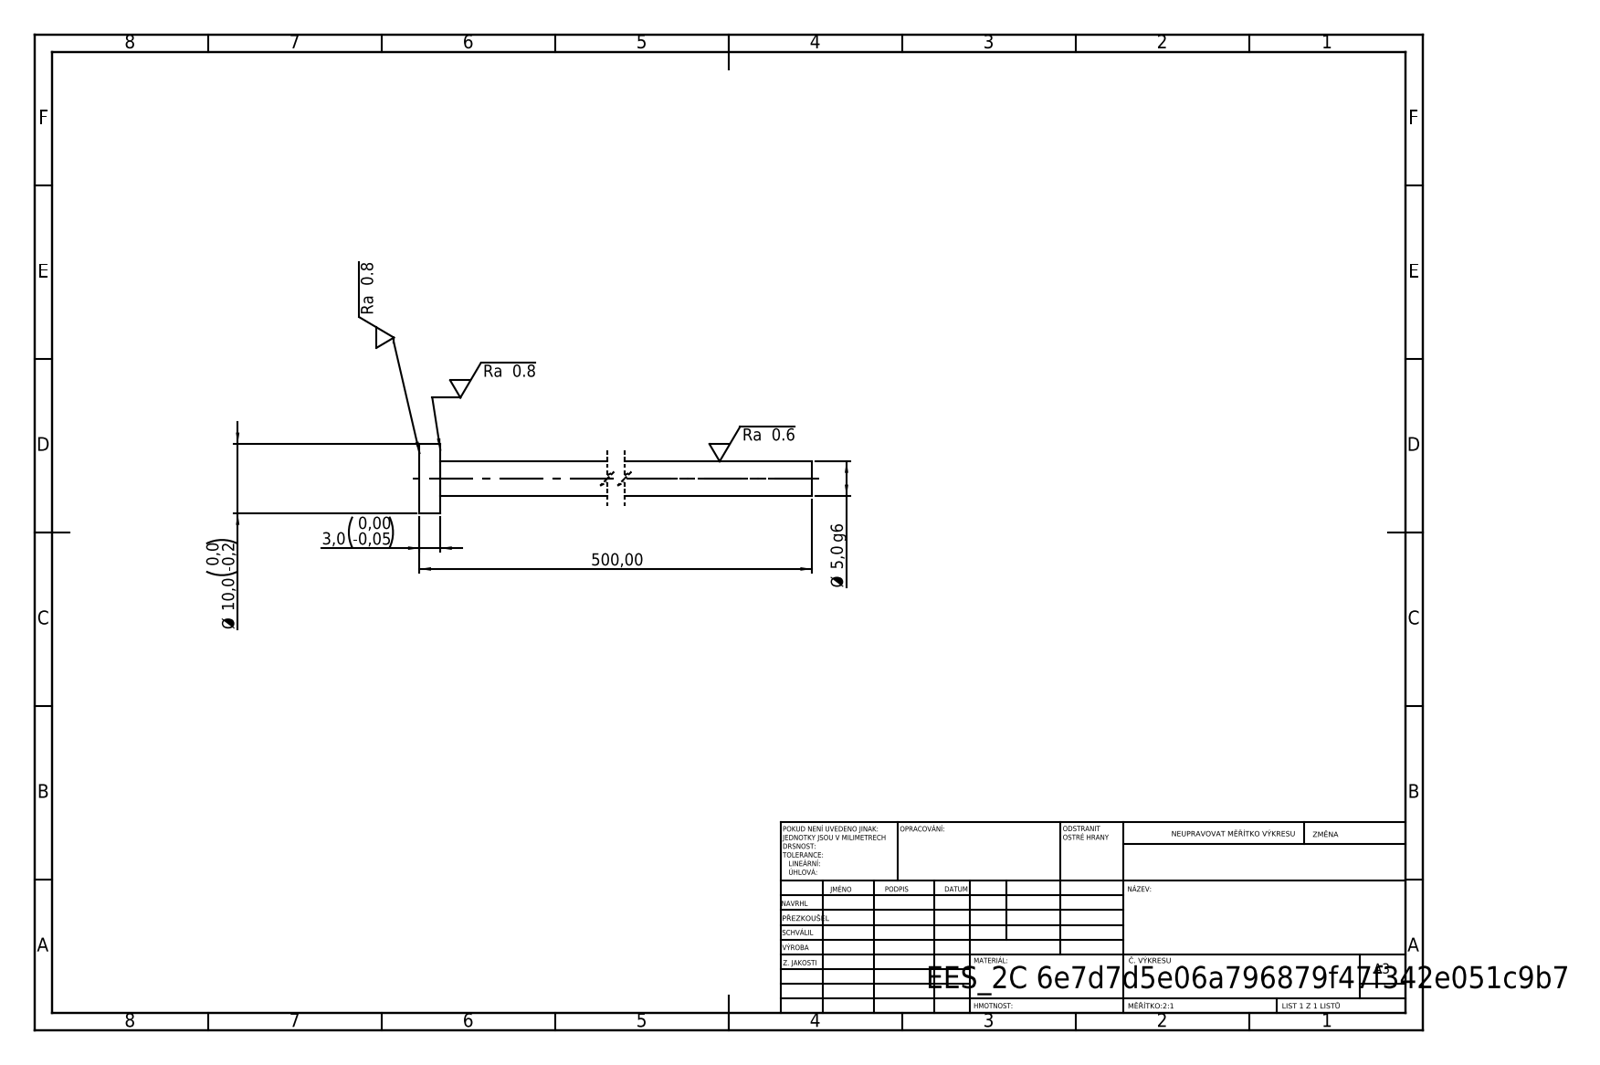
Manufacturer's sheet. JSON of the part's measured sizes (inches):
{"step_written_by": "SolidWorks 2019 (CONFIG_CONTROL_DESIGN)", "units": "inches", "bodies": {"solids": 1, "faces": 7, "planar": 3, "cylindrical": 4, "other": 0}, "overall_size": [19.685, 0.394, 0.394], "volume_in3": 0.61, "surface_area_in2": 12.49, "round_bosses_or_shafts": [[0.394, 1], [0.197, 1]], "face_to_face_distances": [0.118, 19.685, 19.567]}
